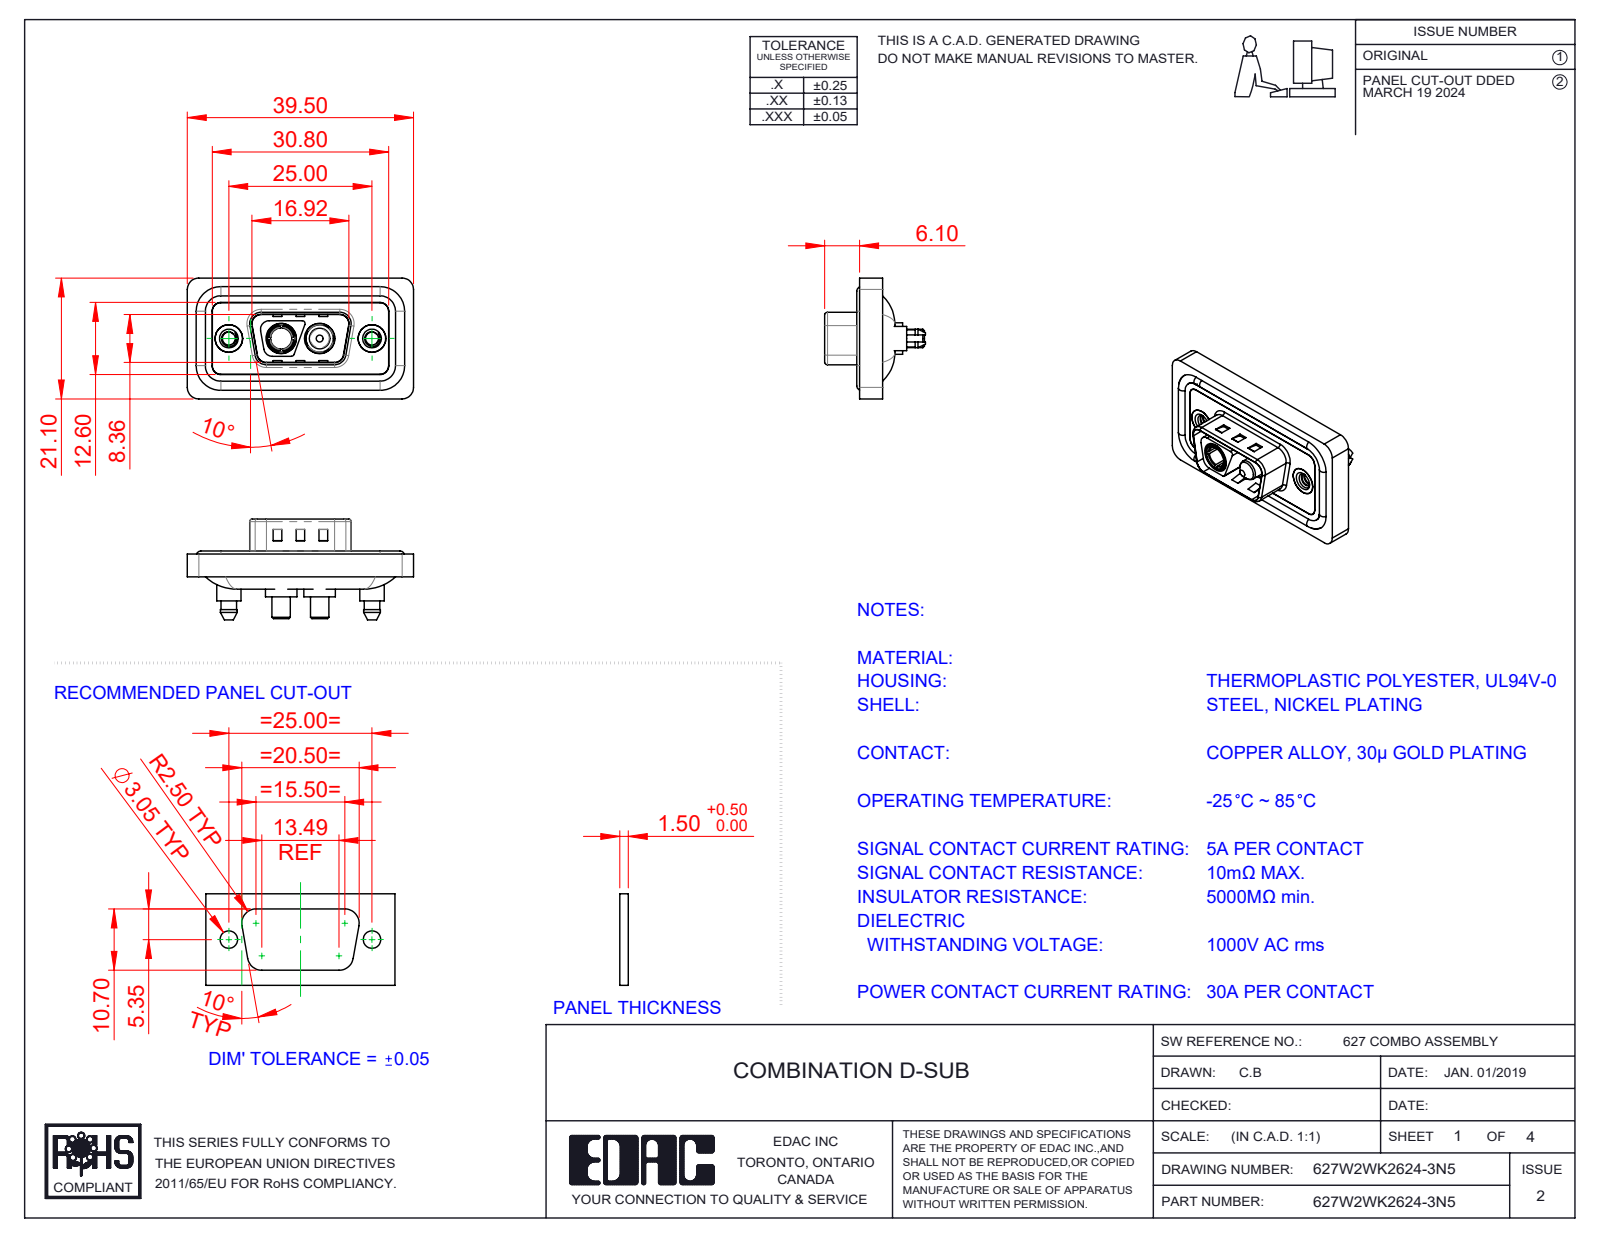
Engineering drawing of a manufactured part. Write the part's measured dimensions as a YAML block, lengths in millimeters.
part_name: "Power Pin_30A S; 627W2WK2624-3N5; 627Combo Housing_2WK2; Power Socket_30A S (+4 more)"
step_written_by: "SolidWorks 2023 (CONFIG_CONTROL_DESIGN)"
units: millimeters
bodies: {solids: 11, faces: 584, planar: 205, cylindrical: 259, other: 120}
overall_size: [39.5, 21.1, 17.6]
volume: 4702
surface_area: 7685
round_holes:
  - {diameter: 2.26, count: 2}
  - {diameter: 4, count: 2}
  - {diameter: 4.8, count: 2}
  - {diameter: 4.85, count: 2}
  - {diameter: 5, count: 2}
  - {diameter: 5.3, count: 2}
  - {diameter: 3.7, count: 1}
round_bosses_or_shafts:
  - {diameter: 1.6, count: 4}
  - {diameter: 5.5, count: 2}
  - {diameter: 5.4, count: 2}
  - {diameter: 5.2, count: 2}
  - {diameter: 4.9, count: 2}
  - {diameter: 4.75, count: 2}
  - {diameter: 4.25, count: 2}
  - {diameter: 3.75, count: 2}
partial_cylinders:
  - {radius: 1.5, count: 26}
  - {radius: 2, count: 18}
  - {radius: 0.5, count: 10}
  - {radius: 1.6, count: 10}
  - {radius: 0.25, count: 4}
  - {radius: 0.6, count: 4}
  - {radius: 0.65, count: 4}
  - {radius: 0.9, count: 4}
face_to_face_distances: [0.4, 1.1, 2.9, 3.1, 0.5, 1.6, 1.5, 4, 1.8, 3.2]
hole_center_spacings: [9.14, 15.86, 6.72, 25]
